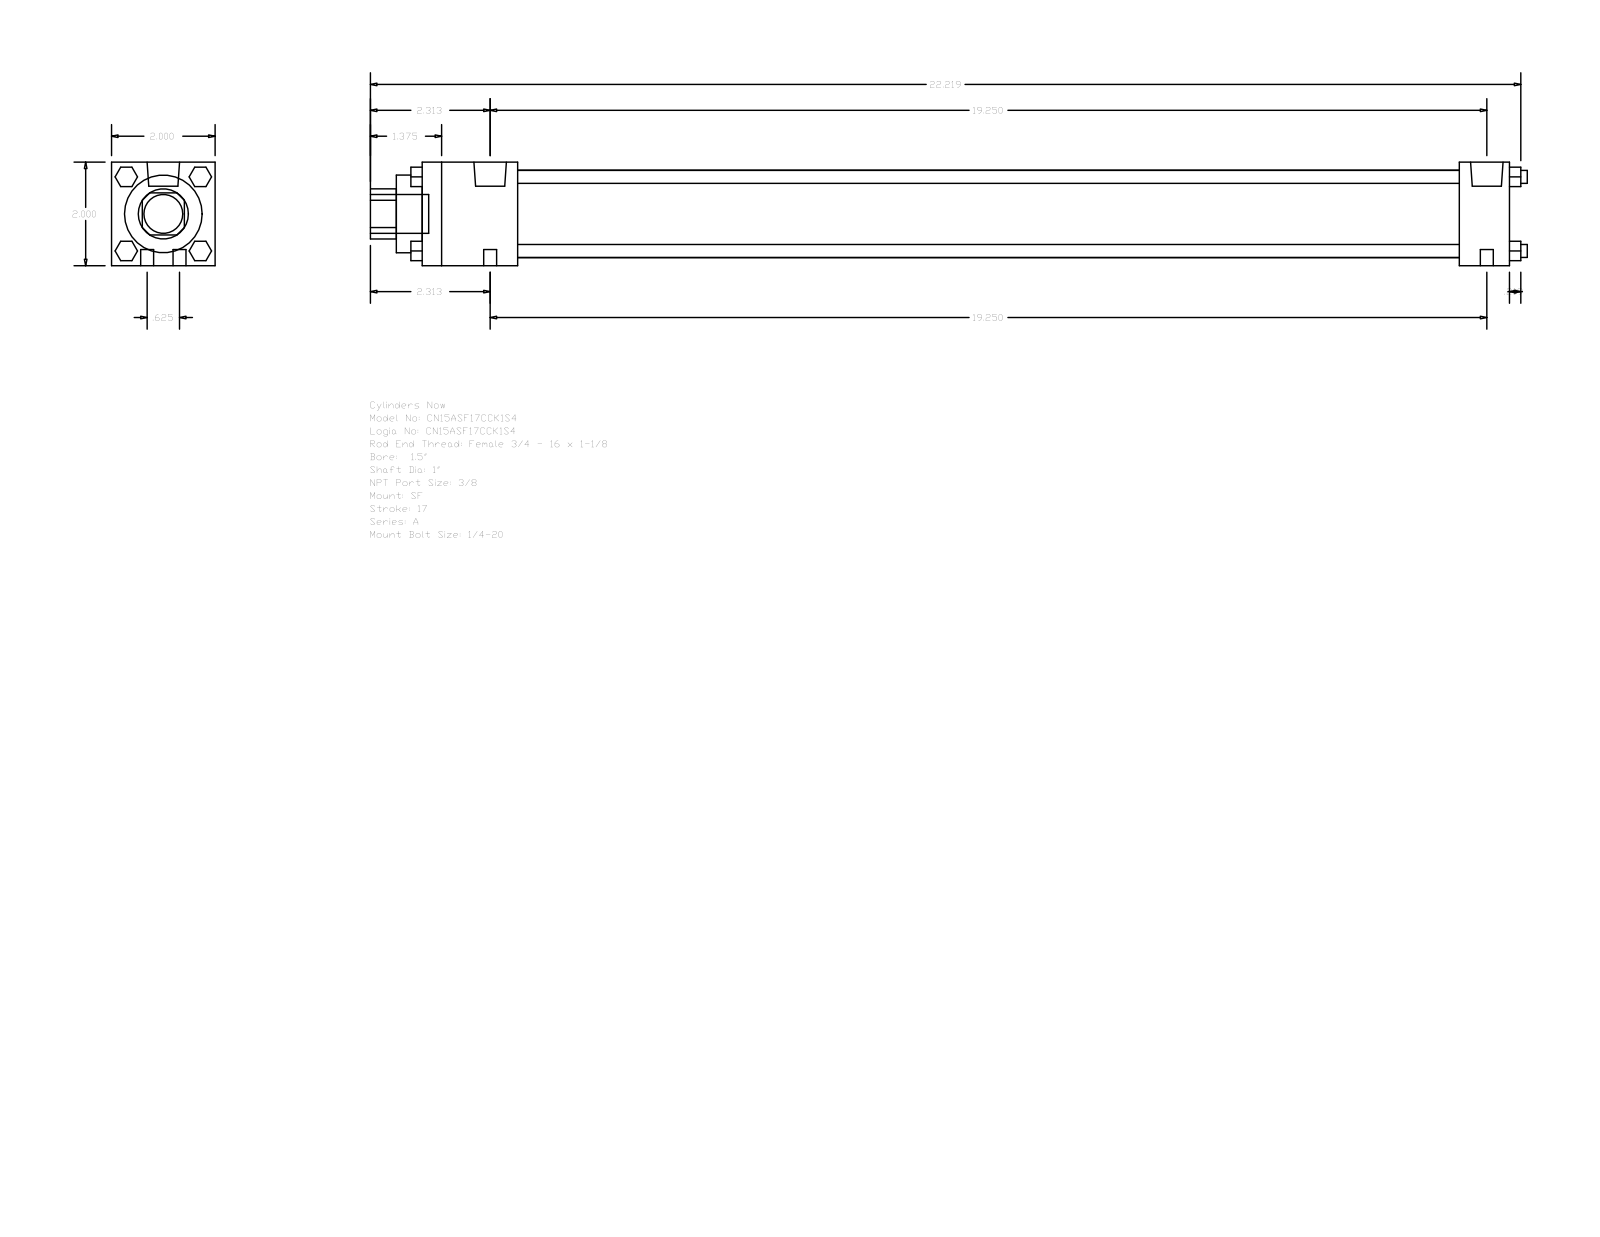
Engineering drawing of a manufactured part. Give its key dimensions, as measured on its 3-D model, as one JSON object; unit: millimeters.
{"part_name": "A_SF__0150_1", "step_written_by": "GSSL Pune (CONFIG_CONTROL_DESIGN)", "units": "millimeters", "bodies": {"solids": 0, "faces": 124, "planar": 94, "cylindrical": 30, "other": 0}, "overall_size": [567.53, 50.8, 50.8], "round_holes": [[25.4, 1], [38.1, 1], [42.93, 1]], "round_bosses_or_shafts": [[6.35, 8], [15.93, 2], [5.56, 2], [19.05, 1]], "partial_cylinders_radius": [[12.29, 1]], "face_to_face_distances": [50.8, 533.4, 46.83, 508.79, 461.96, 486.57, 24.61, 12.7, 59.53, 521.49]}
